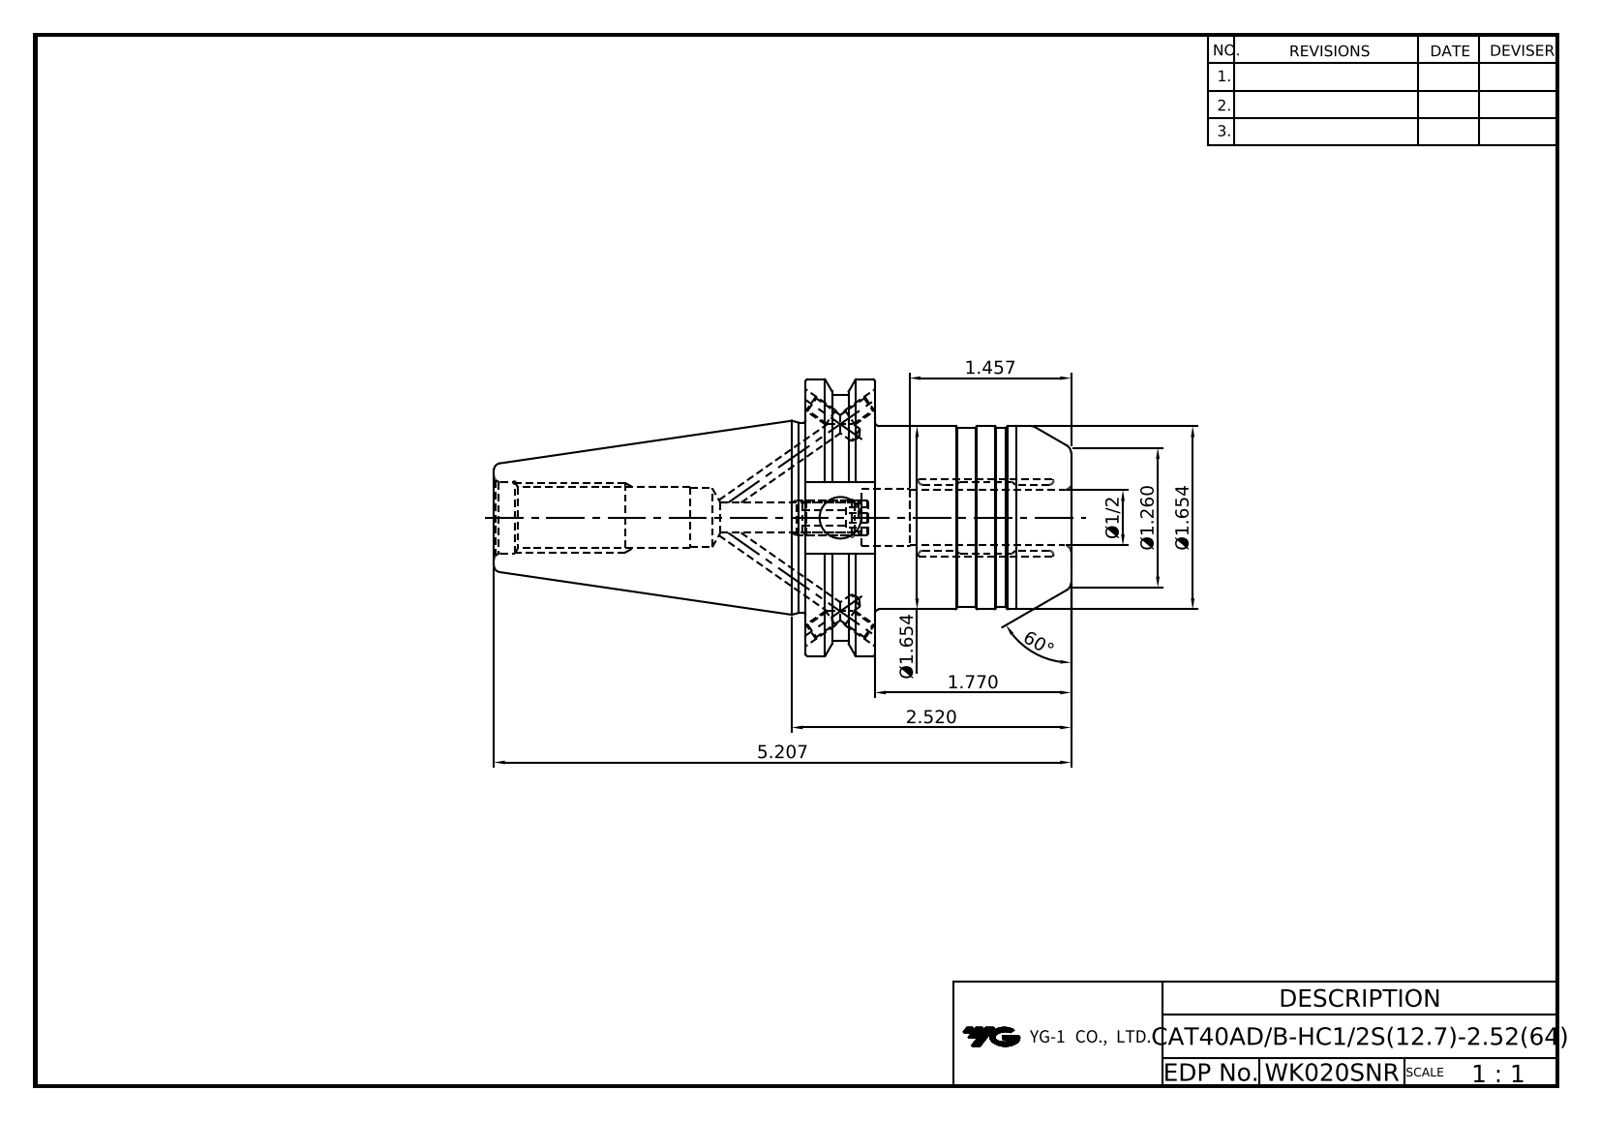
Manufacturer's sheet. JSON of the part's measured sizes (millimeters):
{"part_name": "LO-CAT40ADB-HC12.7S-64", "step_written_by": "Autodesk Inventor 2025 (AUTOMOTIVE_DESIGN)", "units": "millimeters", "bodies": {"solids": 1, "faces": 96, "planar": 33, "cylindrical": 30, "other": 33}, "overall_size": [132.25, 63.5, 61.09], "volume_mm3": 157053, "surface_area_mm2": 27760, "round_holes": [[3.24, 4], [4, 4], [6.92, 1], [9.53, 1], [12.7, 1], [13.2, 1], [13.39, 1], [16.3, 1]], "round_bosses_or_shafts": [[63.5, 1], [56.3, 1], [43.6, 1], [42, 1], [41, 1]], "face_to_face_distances": [15.88, 60.83, 44.95, 47.6, 16.38, 71.42, 87.3, 132.25, 77.47, 81.3], "hole_center_spacings": [35.13]}
